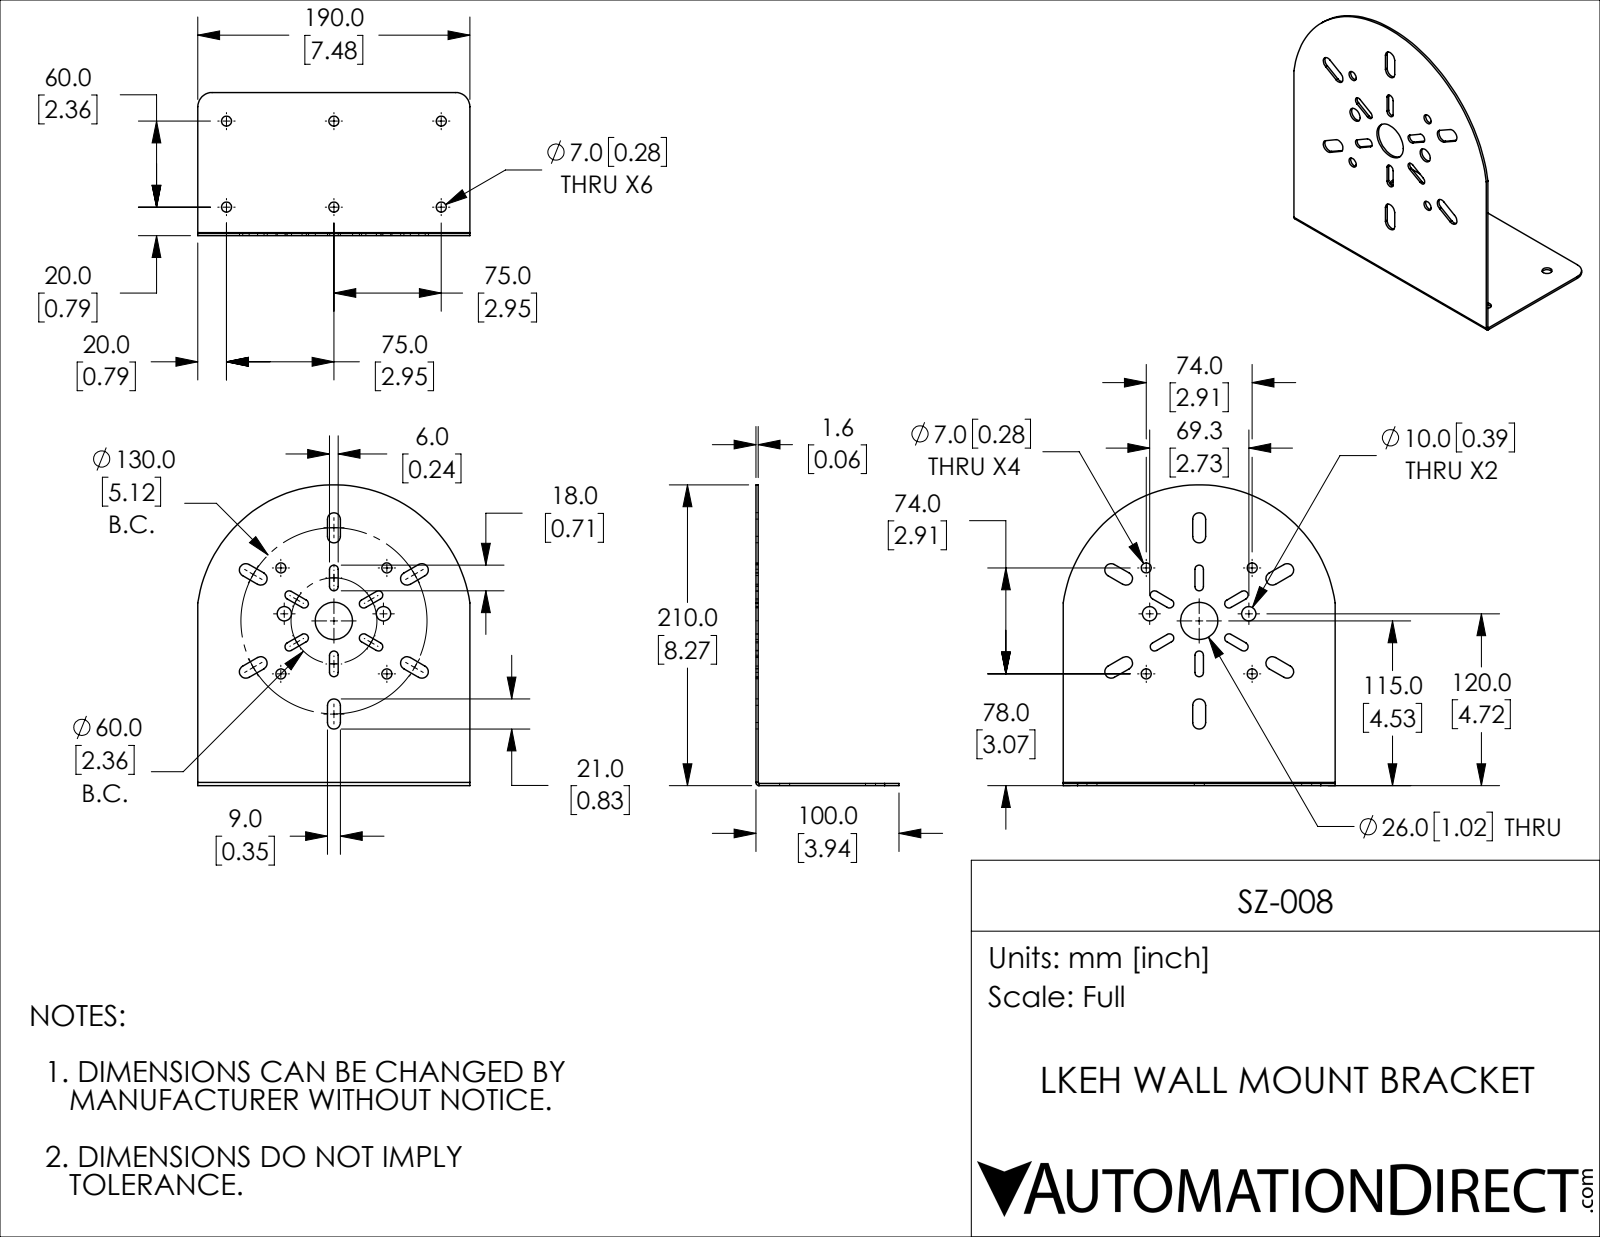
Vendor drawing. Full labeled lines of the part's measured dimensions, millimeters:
Part name (STEP PRODUCT): SZ-008
STEP written by: SolidWorks 2018 (AUTOMOTIVE_DESIGN)
Units: millimetres
Bodies: 1 solid, 98 faces (35 planar, 63 cylindrical, 0 other)
Overall size (bounding box): 210 × 190 × 100
Volume: 83 120 mm³ · Surface area: 106 800 mm²
Round holes (diameter × count): ⌀7 ×10, ⌀10 ×2, ⌀26 ×1
Partial cylindrical surfaces — rounded edges, fillets, slot ends (radius × count): R3 ×12, R4.5 ×12, R10 ×2, R0.6 ×1, R2.2 ×1, R95.9 ×1
Main face-to-face distances: 1.6, 190, 98.4, 100, 7.5, 1.5, 6, 9, 92, 98
Hole centre spacings: 52.3, 74, 75, 96, 60, 32.1, 35, 42.1
